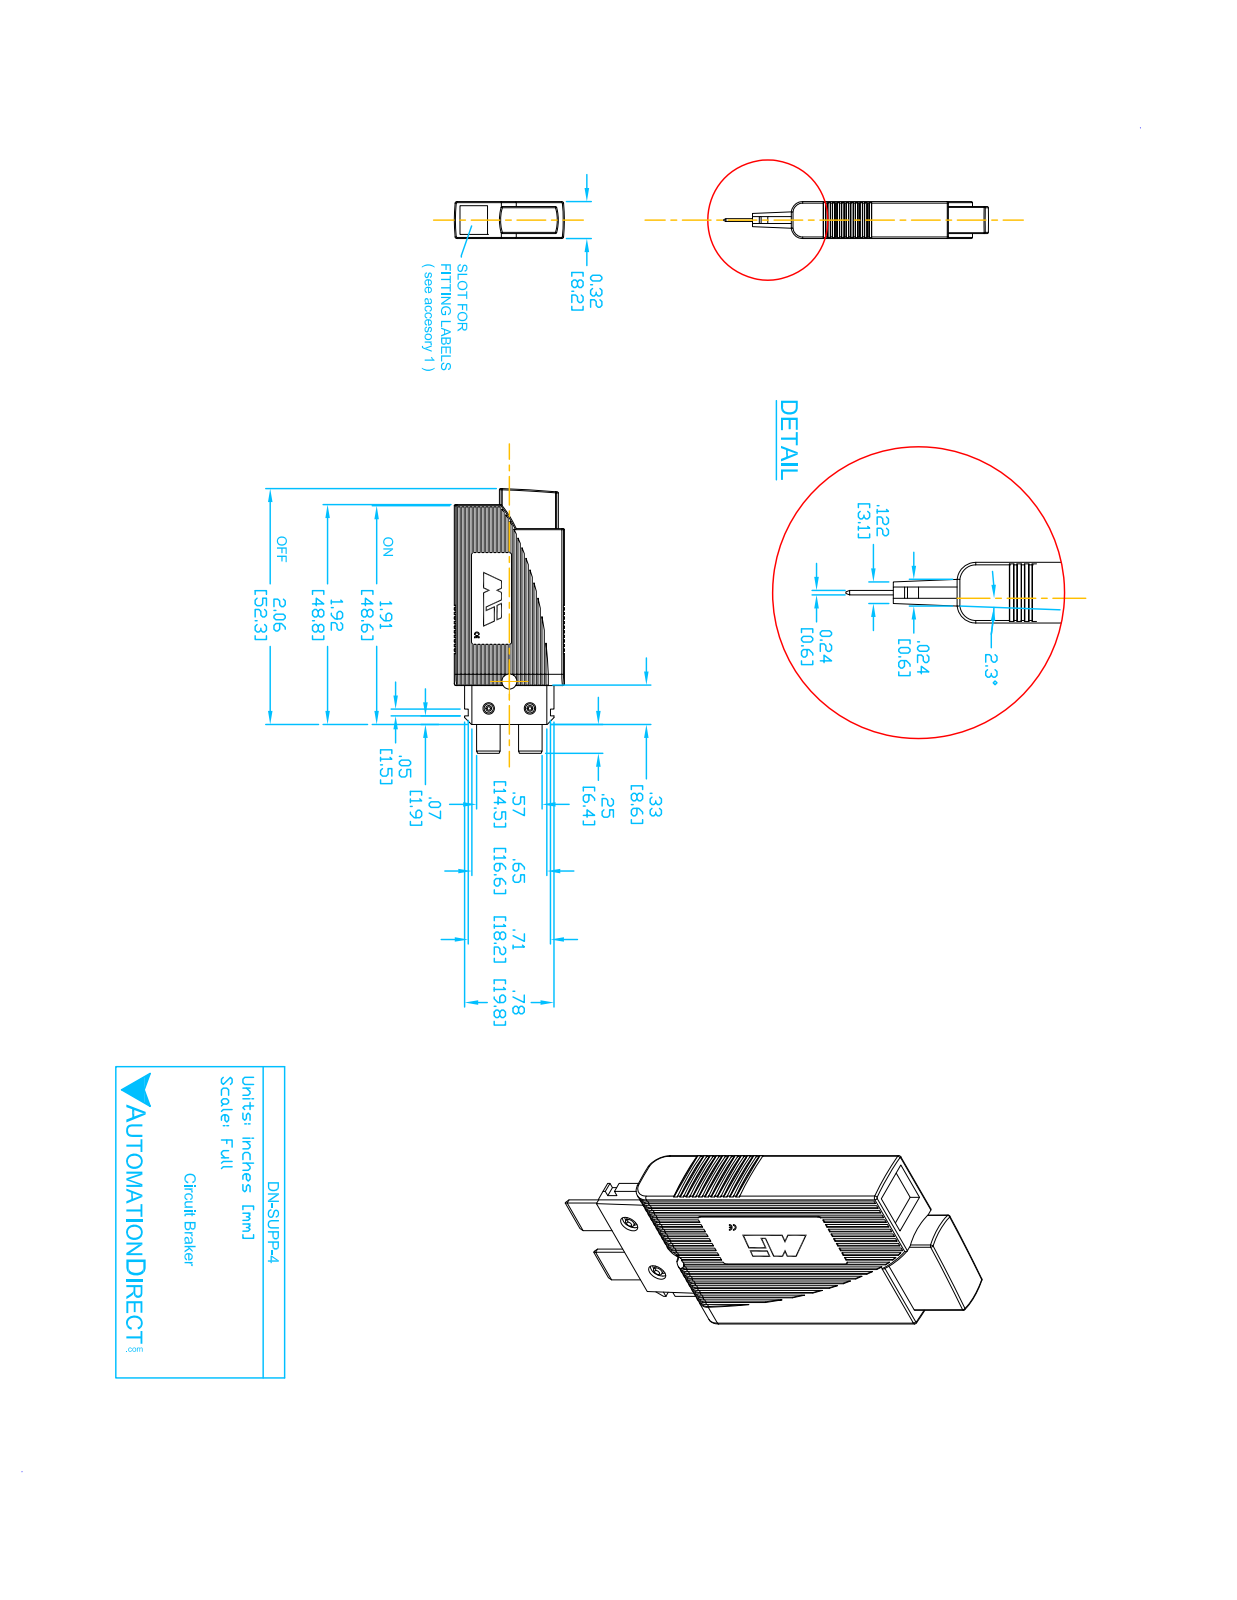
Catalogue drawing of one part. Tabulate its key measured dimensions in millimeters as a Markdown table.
| quantity | value |
| --- | --- |
| part name | DN-SUPP-4 |
| STEP written by | SolidWorks 2017 (AUTOMOTIVE_DESIGN) |
| units | millimeters |
| bodies | 1 solid, 95 faces (47 planar, 28 cylindrical, 20 other) |
| overall size | 55.4 × 24.4 × 8.2 |
| volume | 8 280 mm³ |
| surface area | 3 375 mm² |
| partial cylindrical surfaces (radius × count) | 0.3 × 21, 4 × 2, 55 × 1, 59.2 × 1, 60 × 1 |
| main face-to-face distances | 8.2, 24.4, 3.8, 4.4, 0.8, 7.4, 3, 3.6, 0.6, 3.6 |
